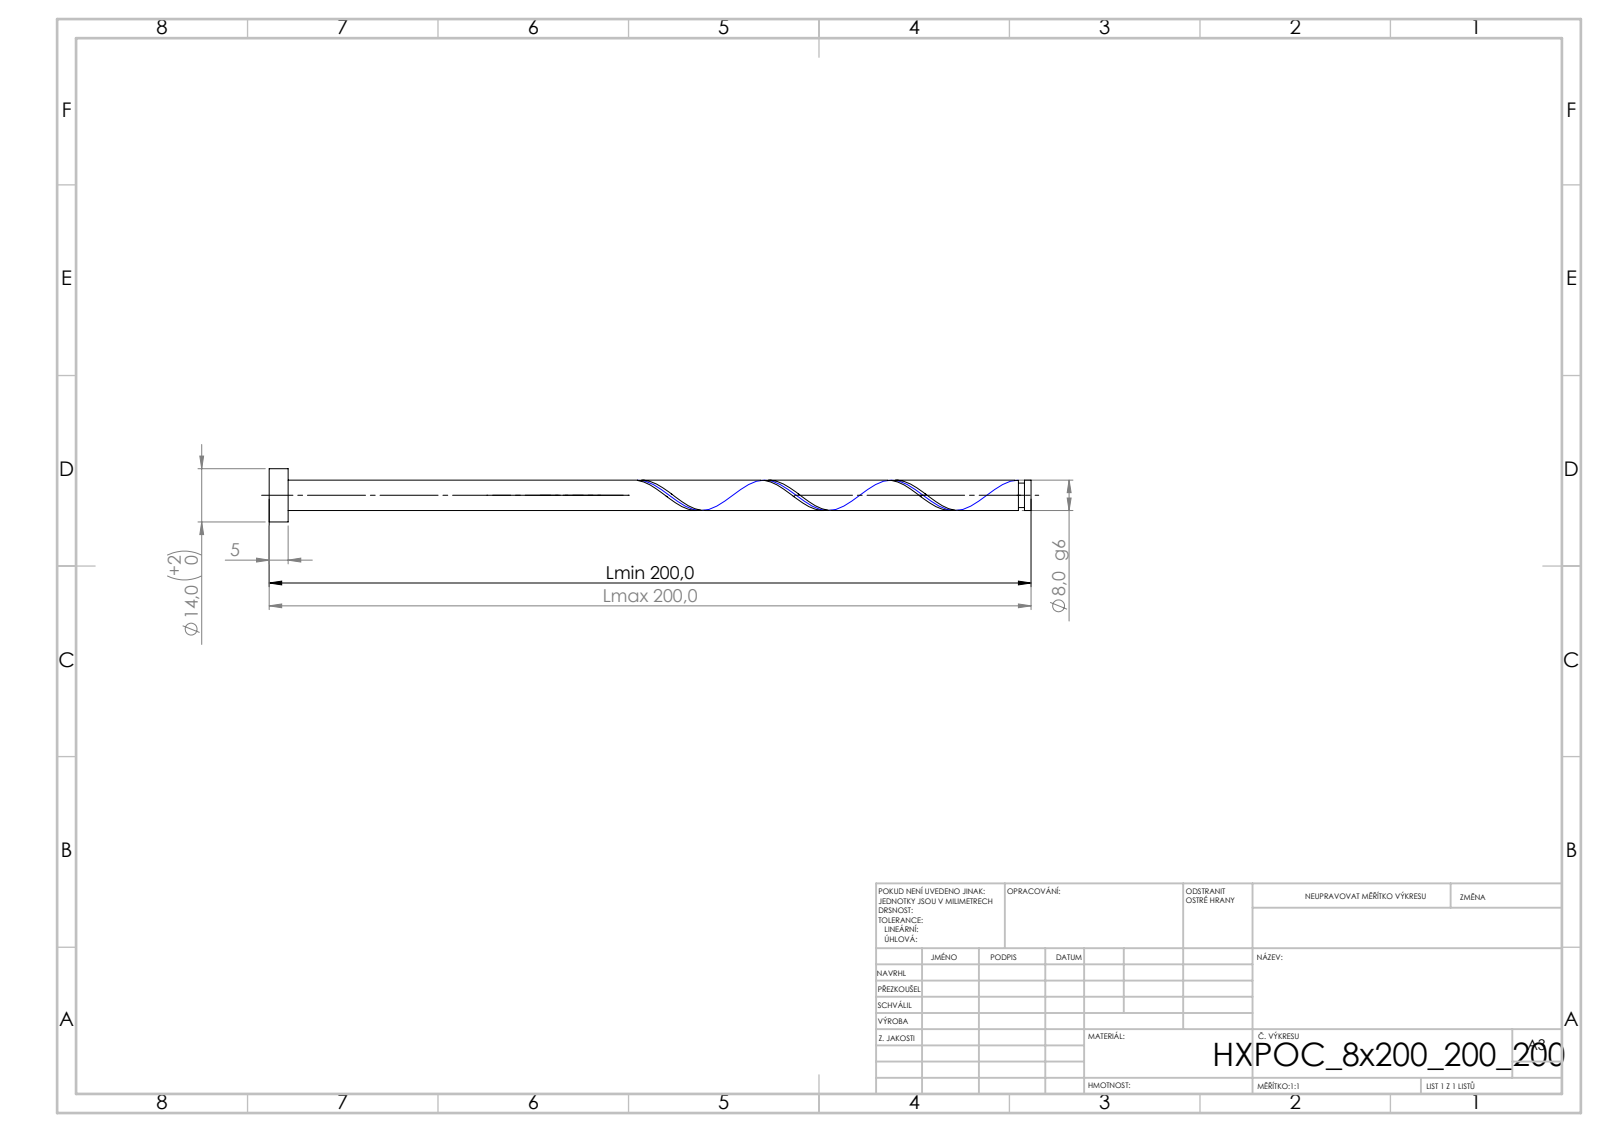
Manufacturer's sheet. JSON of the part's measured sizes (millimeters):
{"step_written_by": "SolidWorks 2019 (CONFIG_CONTROL_DESIGN)", "units": "millimeters", "bodies": {"solids": 1, "faces": 21, "planar": 6, "cylindrical": 14, "other": 1}, "overall_size": [200, 14, 14], "volume_mm3": 10446, "surface_area_mm2": 5560, "round_bosses_or_shafts": [[14, 1], [8, 1], [6.4, 1]], "face_to_face_distances": [5, 200, 195, 198.28, 193.28, 1.72, 196.68, 191.68, 1.6, 3.32]}
